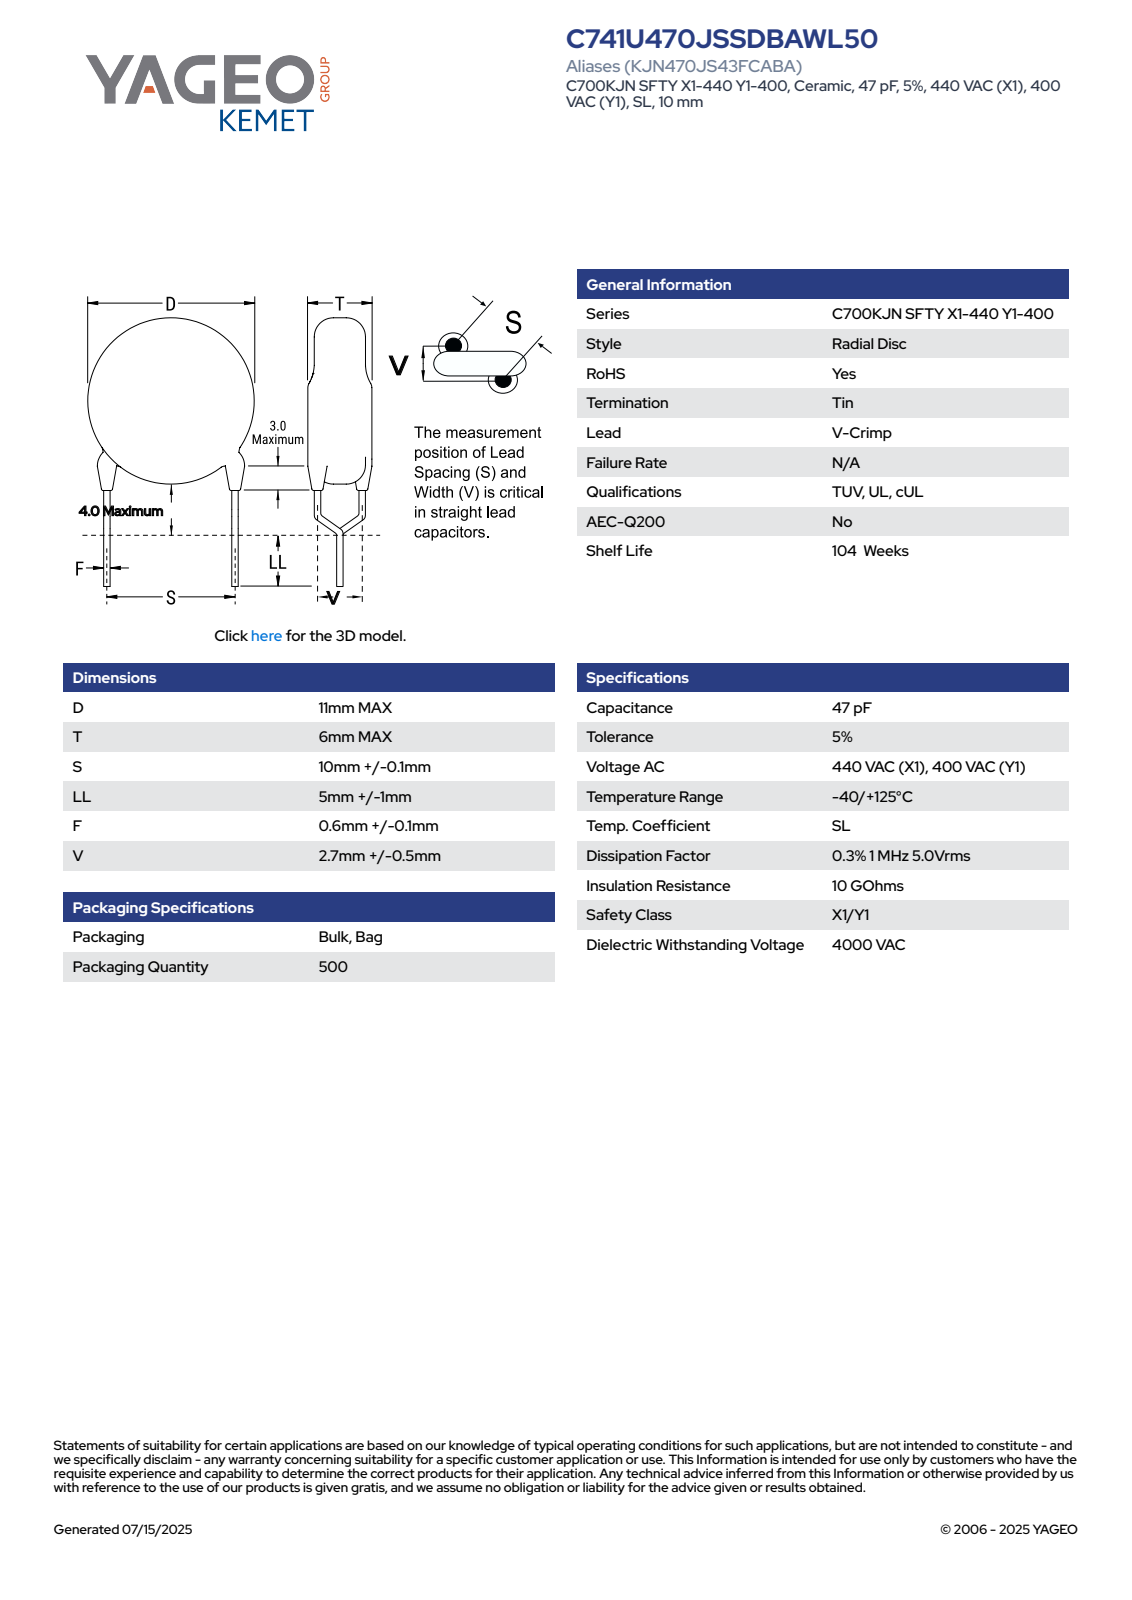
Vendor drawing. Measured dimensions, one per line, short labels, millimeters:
name: CCD_VC11X6_D11T6S10LL6F0.7V2.7
written by: SolidWorks 2021 (AUTOMOTIVE_DESIGN)
unit: mm
bodies: 4 solids, 89 faces (63 planar, 22 cylindrical, 4 other)
size: 17 × 11.2 × 6
volume: 568 mm³; area: 423 mm²
bosses: 6× ⌀0.7, 4× ⌀1.2, 1× ⌀11
face distances: 6, 0.97, 12.01, 6.01, 11.04, 5.04, 0.42, 0.6, 3.96, 2
